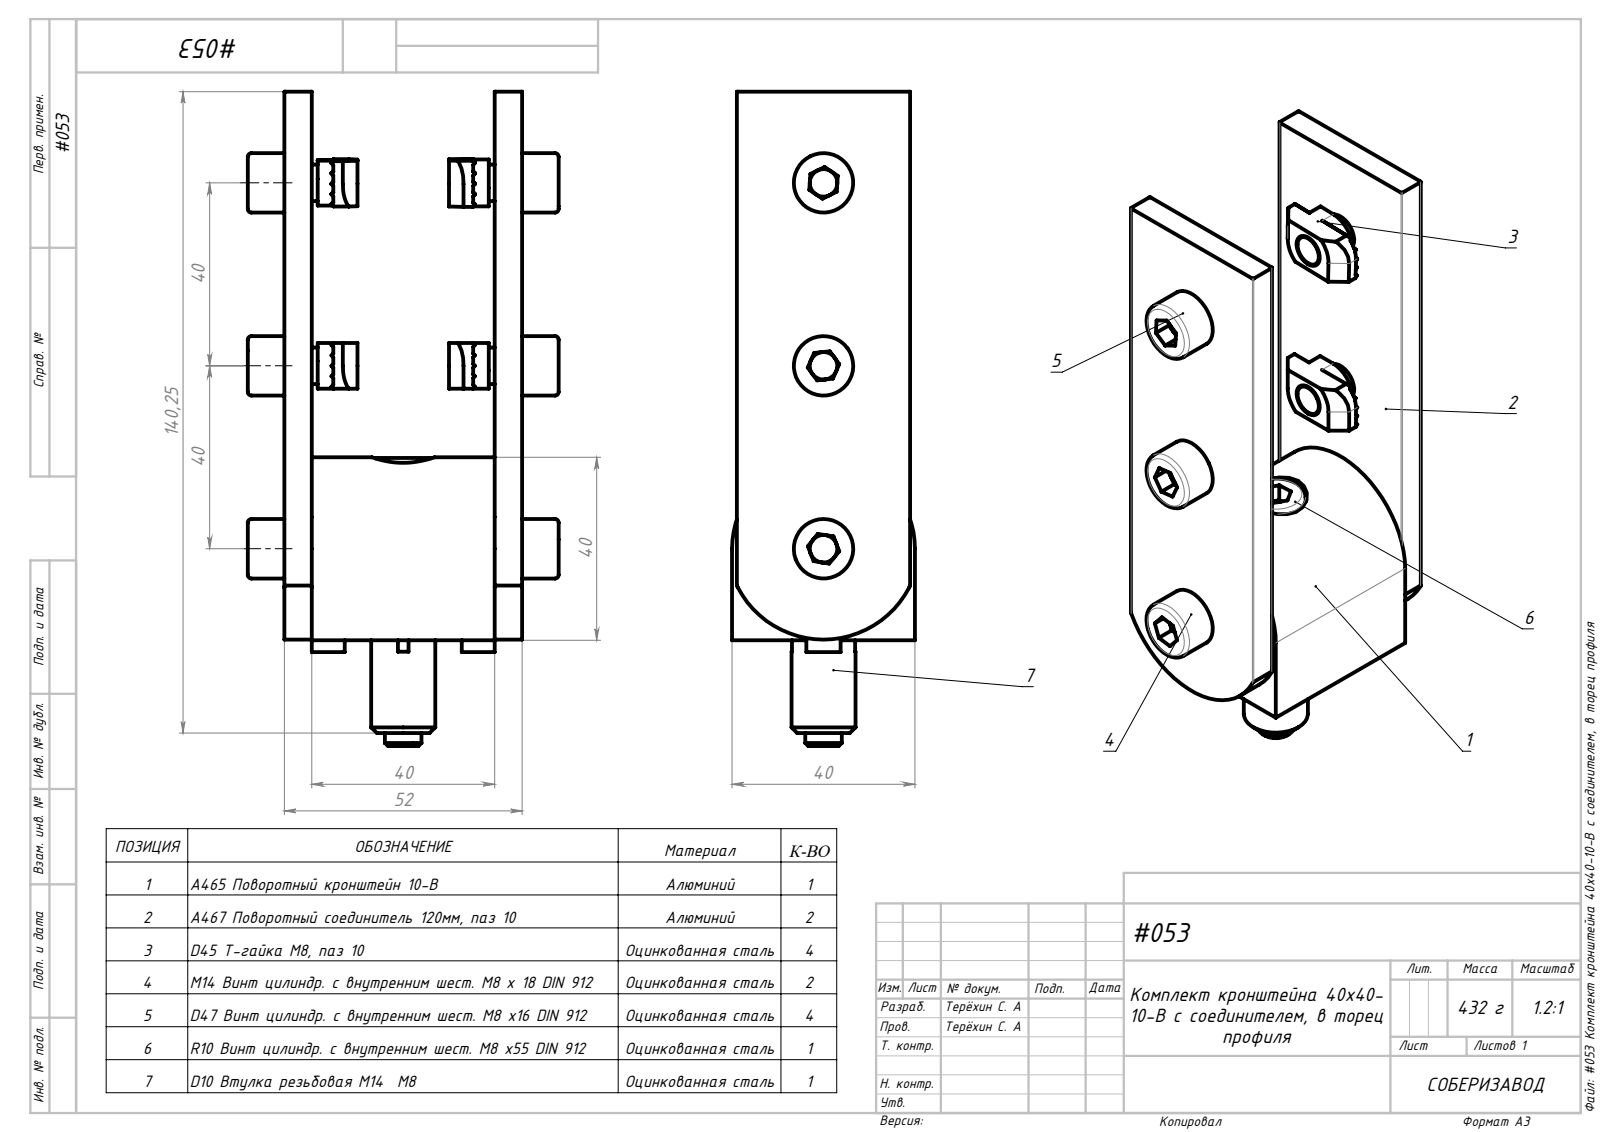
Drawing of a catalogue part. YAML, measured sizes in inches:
part_name: "#053 Комплект кронштейна 40х40-10-В с соединителем, в торец профиля; D45 Т-гайка М8, паз 10_00; A465 Поворотный кронштейн 10-B; D47 Винт цилиндр. с внутренним шест. М8 х16 DIN 912 (+4 more)"
step_written_by: "SolidWorks 2021 (AUTOMOTIVE_DESIGN)"
units: inches
bodies: {solids: 15, faces: 479, planar: 290, cylindrical: 87, other: 102}
overall_size: [5.634, 2.677, 1.575]
volume: 7.573
surface_area: 69.87
round_holes:
  - {diameter: 0.335, count: 4}
  - {diameter: 0.264, count: 2}
  - {diameter: 0.256, count: 1}
  - {diameter: 0.276, count: 1}
  - {diameter: 0.539, count: 1}
round_bosses_or_shafts:
  - {diameter: 0.512, count: 4}
  - {diameter: 0.315, count: 4}
  - {diameter: 0.551, count: 1}
partial_cylinders:
  - {radius: 0.008, count: 8}
  - {radius: 0.236, count: 8}
  - {radius: 0.223, count: 4}
  - {radius: 0.787, count: 1}
  - {radius: 0.831, count: 1}
face_to_face_distances: [0.236, 1.811, 1.575, 2.047, 0.041, 1.533, 1.492, 0.394, 0.315, 0.63]
hole_center_spacings: [1.575, 3.15]
